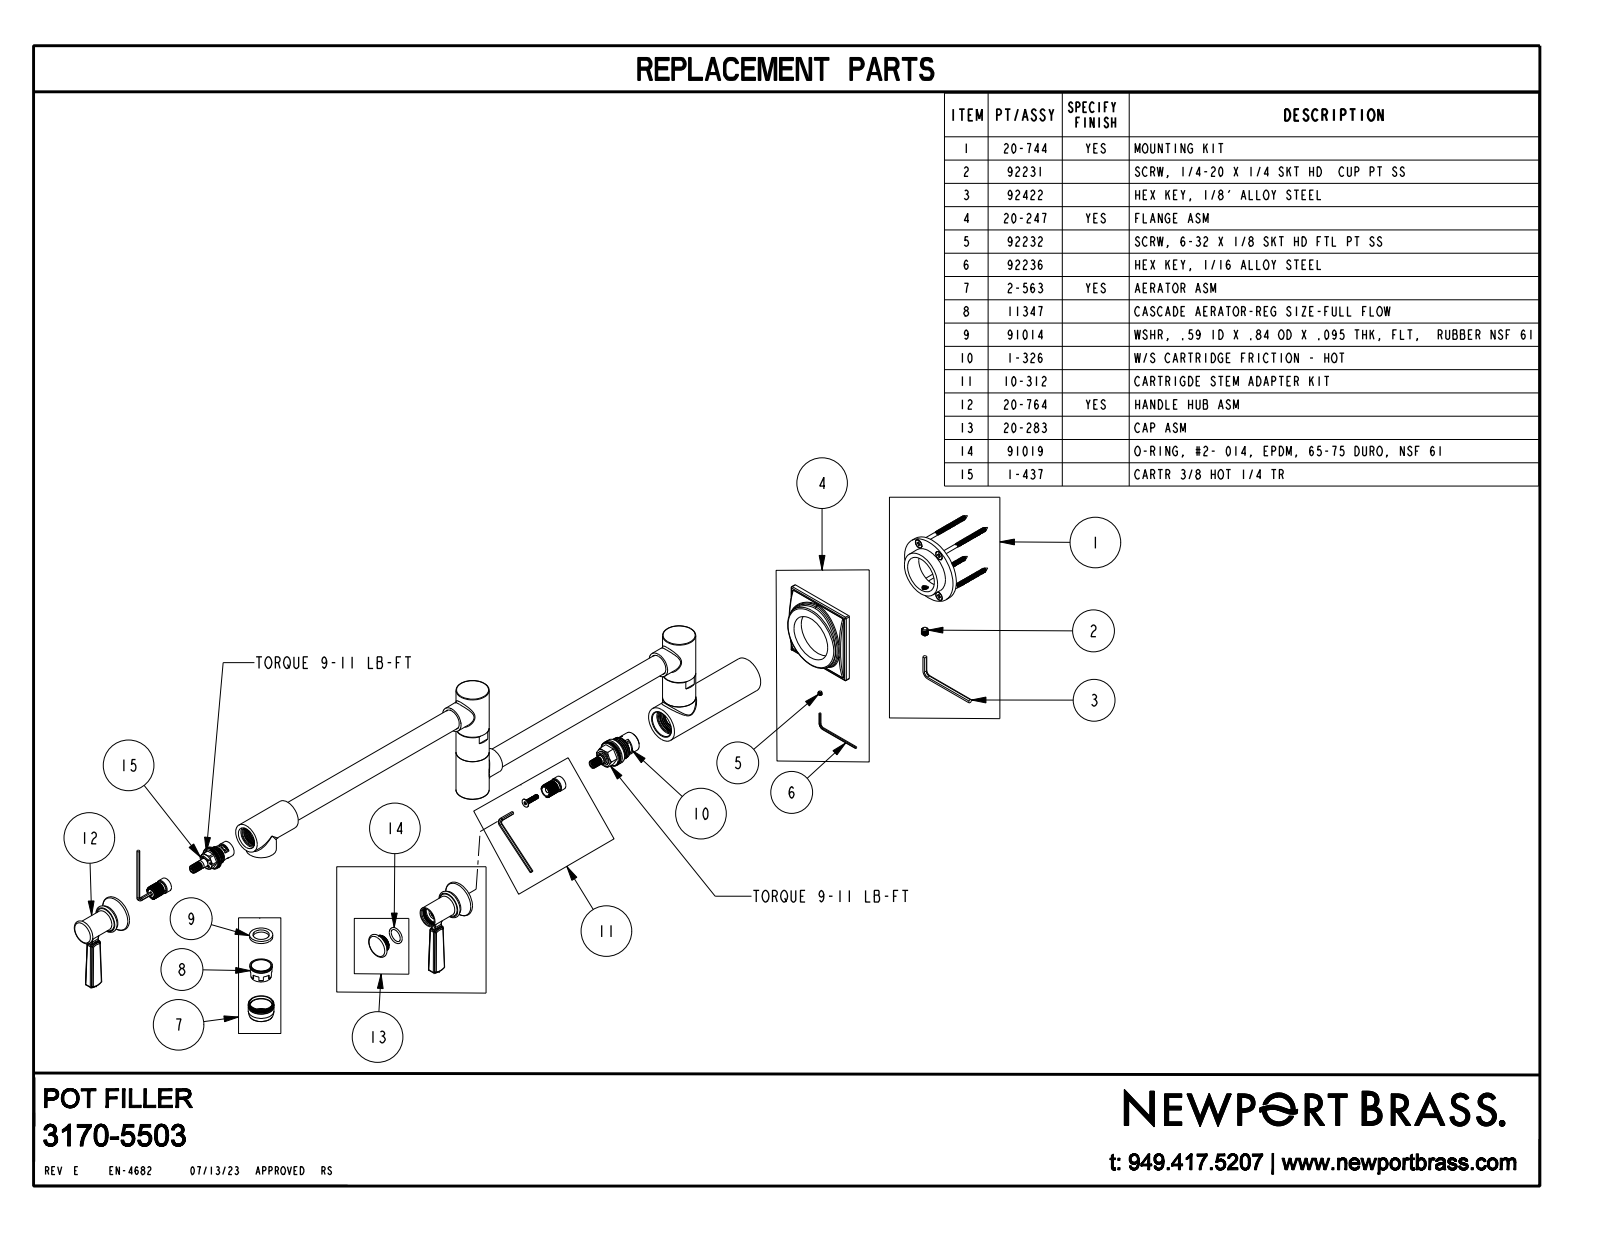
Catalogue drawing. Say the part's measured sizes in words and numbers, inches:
The part is named "3170-5503". Its 3-D file was written by "CREO PARAMETRIC BY PTC INC, 2018400 (CONFIG_CONTROL_DESIGN)". It is 1 solid with 428 faces: 74 planar, 110 cylindrical and 244 other. Overall it measures 27.444 by 8.946 by 2.8 inches. Its volume is 31.07 cubic inches and its surface area 141.1 square inches. Round bosses or shafts: 4 of diameter 0.94, 2 of diameter 1.2, 2 of diameter 1.1, 2 of diameter 0.76, 2 of diameter 0.75, 1 of diameter 2.42, 1 of diameter 1.325, 1 of diameter 0.786. Partial cylindrical surfaces (rounded edges, fillets, slot ends): 24 of radius 0.04, 16 of radius 0.02, 12 of radius 0.03, 8 of radius 0.037, 4 of radius 0.33, 2 of radius 0.45, 2 of radius 0.57, 1 of radius 0.472. The main face-to-face distances are 0.57, 2.86, 2.8, 21.248, 1.576, 4.437, 1.775, 1.676, 3.33, 0.02.
